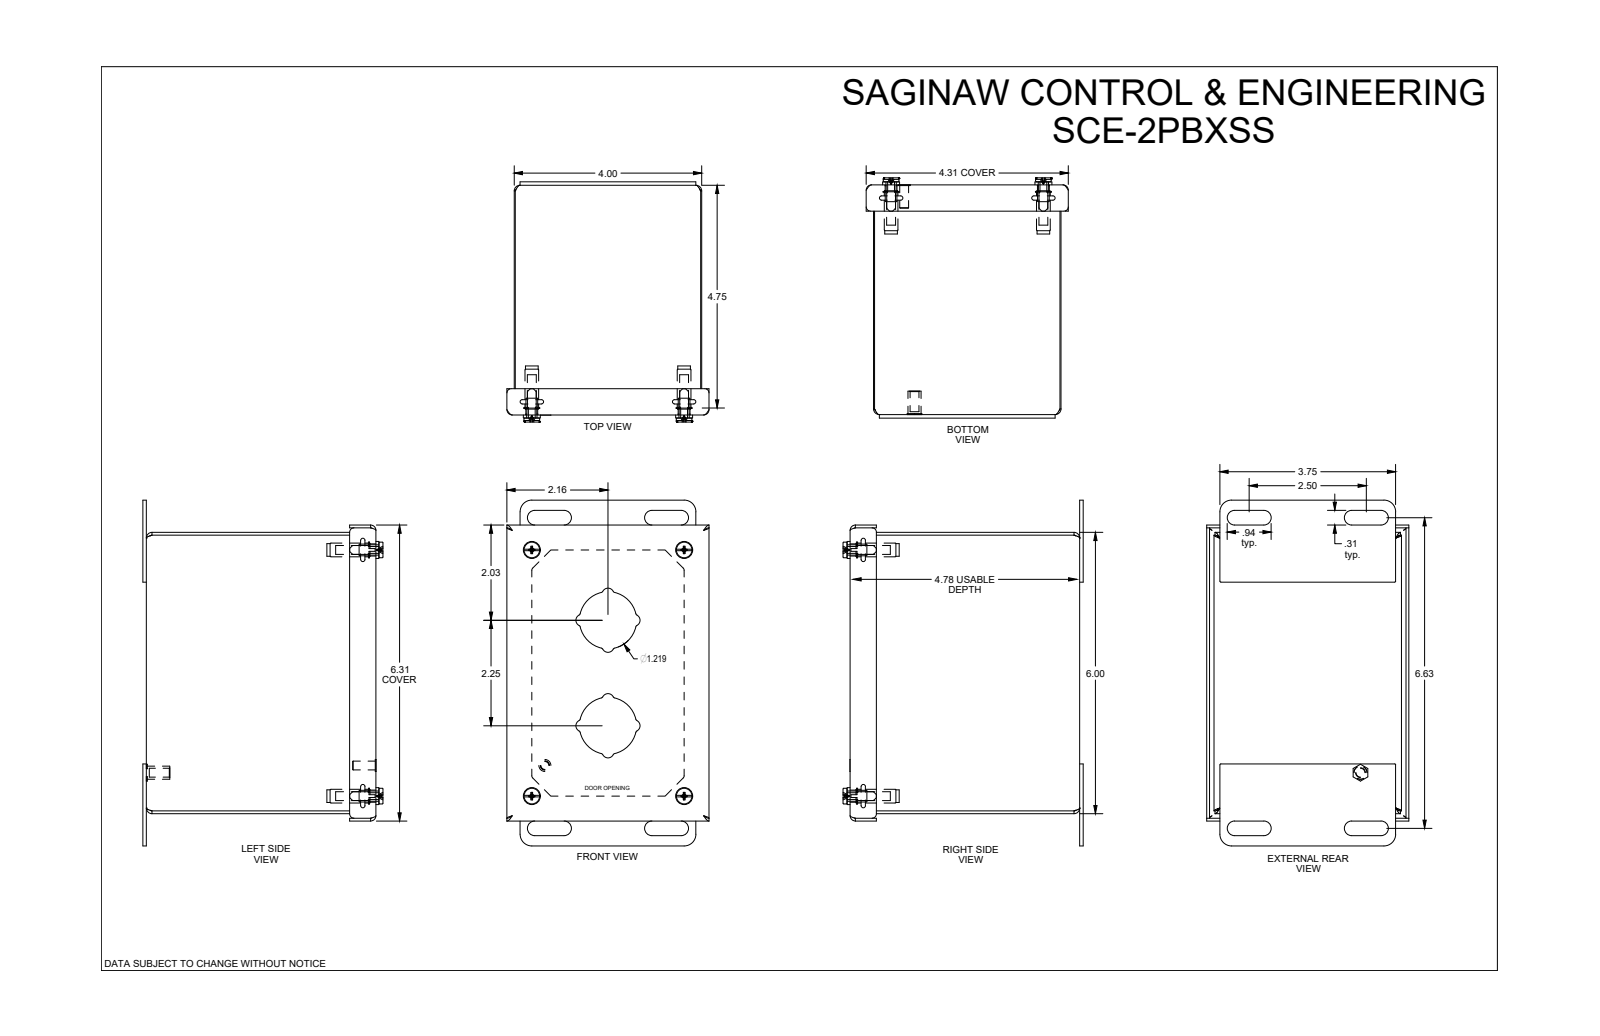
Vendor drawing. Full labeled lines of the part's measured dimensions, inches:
Part name (STEP PRODUCT): SCE-2PBX
STEP written by: SolidWorks 2021 (AUTOMOTIVE_DESIGN)
Units: inches
Bodies: 14 solids, 426 faces (159 planar, 126 cylindrical, 141 other)
Overall size (bounding box): 7.375 × 5.124 × 4.313
Volume: 10.84 in³ · Surface area: 358.1 in²
Round holes (diameter × count): ⌀0.22 ×4
Round bosses / shafts (diameter × count): ⌀0.188 ×5, ⌀0.362 ×4, ⌀0.334 ×4, ⌀0.26 ×4, ⌀0.146 ×4, ⌀0.256 ×1
Partial cylindrical surfaces — rounded edges, fillets, slot ends (radius × count): R0.06 ×24, R0.04 ×16, R0.015 ×8, R0.115 ×8, R0.125 ×8, R0.156 ×8, R0.245 ×8, R0.02 ×4
Main face-to-face distances: 0.06, 3.94, 4.838, 5.94, 4, 3.88, 4.898, 4.778, 6, 5.88
Hole centre spacings: 3.25, 5.25, 6.174
